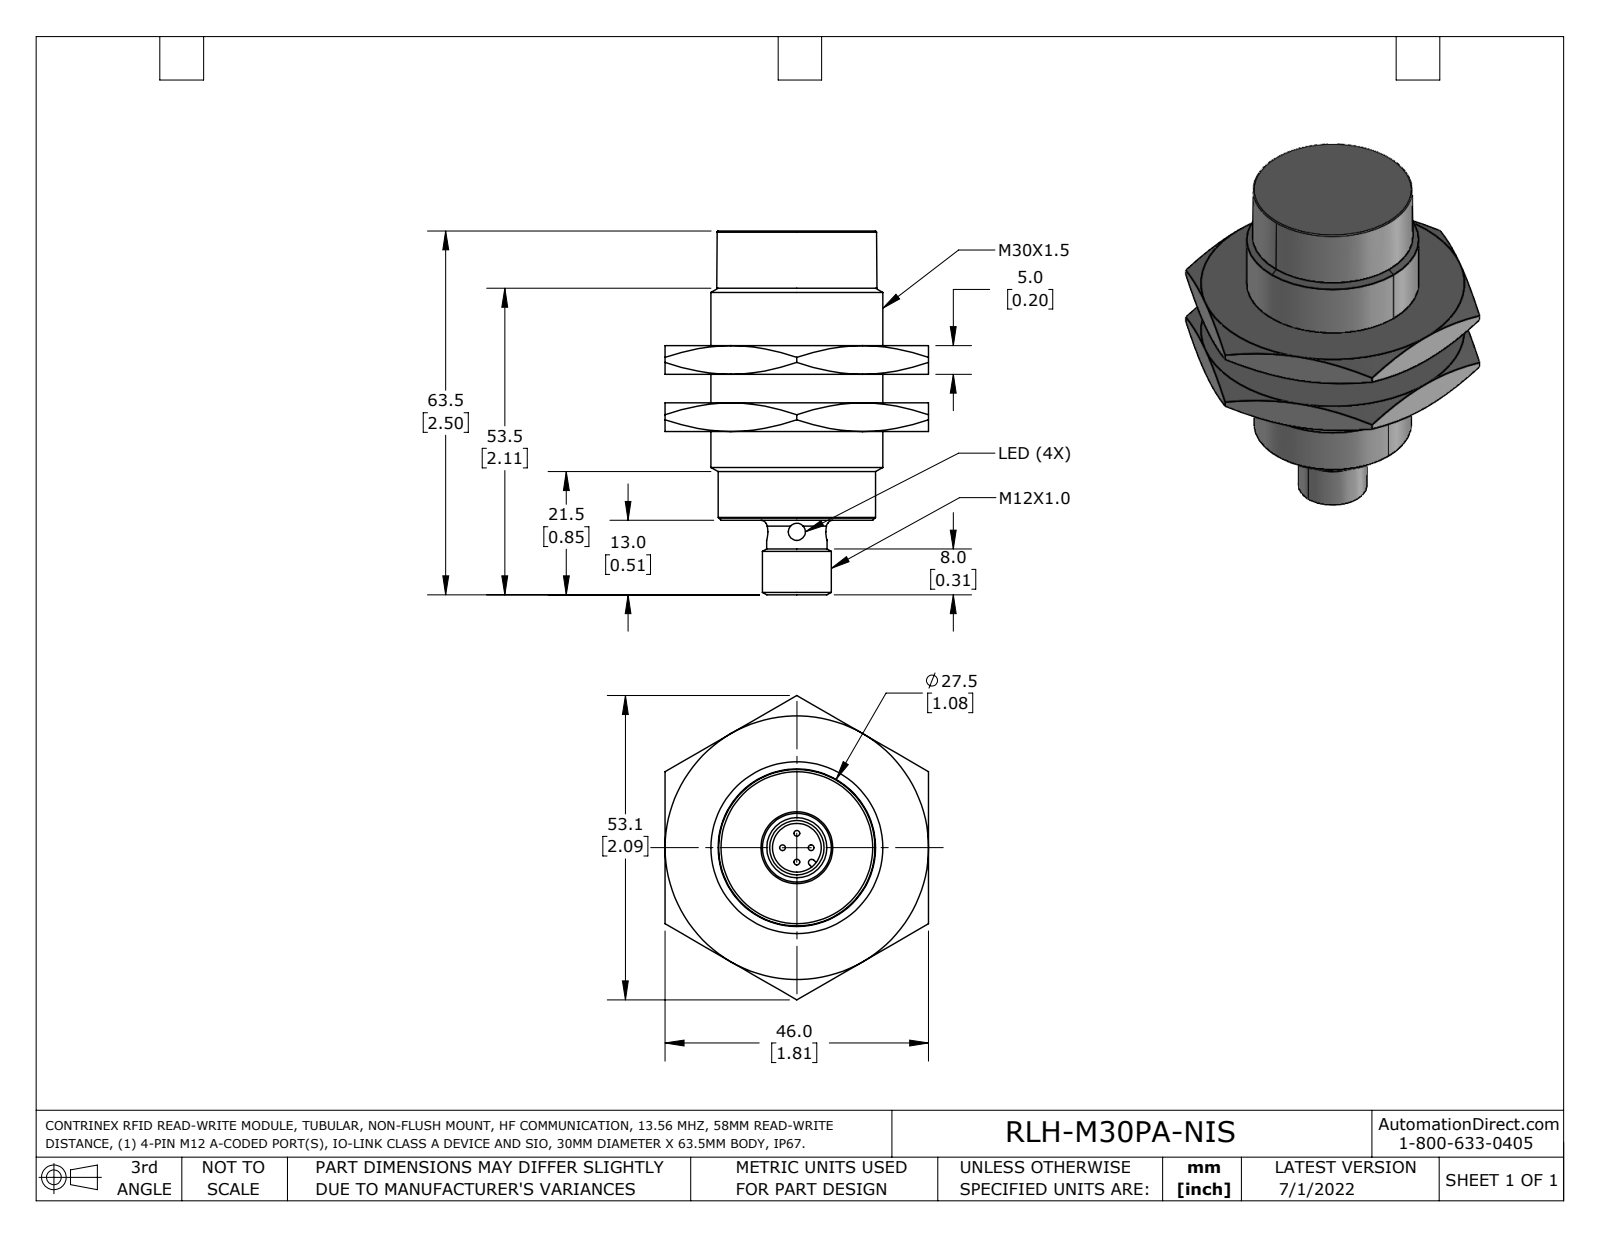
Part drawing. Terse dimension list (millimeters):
name: RLH-M30PA-NIS
written by: SolidWorks 2021 (AUTOMOTIVE_DESIGN)
unit: mm
bodies: 3 solids, 135 faces (25 planar, 41 cylindrical, 69 other)
size: 63.5 × 53.12 × 46
volume: 46 555 mm³; area: 13 697 mm²
holes: 2× ⌀3, 1× ⌀8.5, 1× ⌀26.5
bosses: 4× ⌀1, 1× ⌀30, 1× ⌀27.5, 1× ⌀27.3, 1× ⌀12, 1× ⌀10.55
rounds: 2× R0.5, 1× R0.55
face distances: 5, 10, 15, 20, 25, 30, 35, 46, 50.5, 30.5
